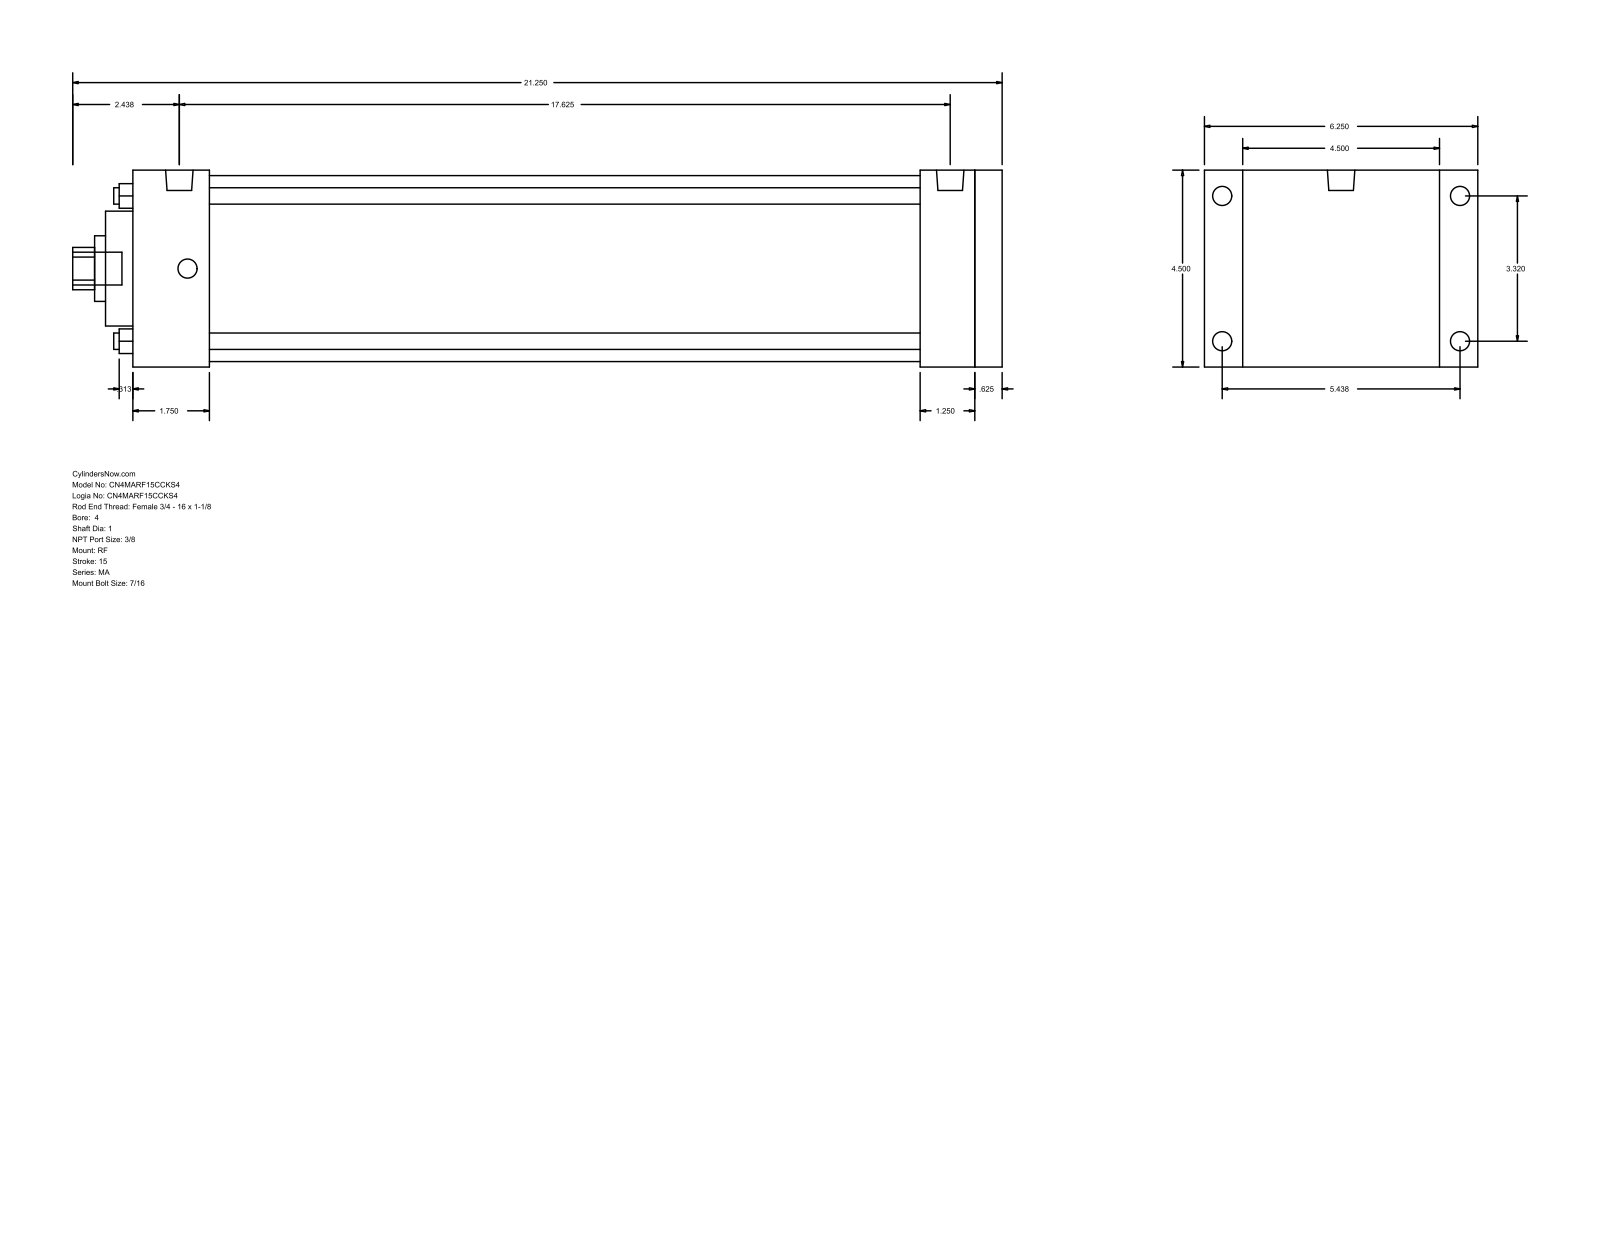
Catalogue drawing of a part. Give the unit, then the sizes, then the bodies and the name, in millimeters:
Units: millimetres
Overall size (bounding box): 539.75 × 158.75 × 114.3
Round holes (diameter × count): ⌀9.53 ×4, ⌀25.4 ×1, ⌀38.1 ×1, ⌀66.67 ×1, ⌀107.95 ×1
Round bosses / shafts (diameter × count): ⌀11.11 ×8, ⌀15.93 ×2, ⌀19.05 ×1
Partial cylindrical surfaces — rounded edges, fillets, slot ends (radius × count): R12.29 ×1
Main face-to-face distances: 114.3, 504.83, 15.87, 488.96, 22.23, 136.53, 457.2, 31.76, 47.63, 44.46
Hole centre spacings: 59.62, 84.32, 119.25
Bodies: 0 solids, 94 faces (65 planar, 29 cylindrical, 0 other)
Part name (STEP PRODUCT): MA_RF__0400_1
STEP written by: GSSL Pune (CONFIG_CONTROL_DESIGN)
